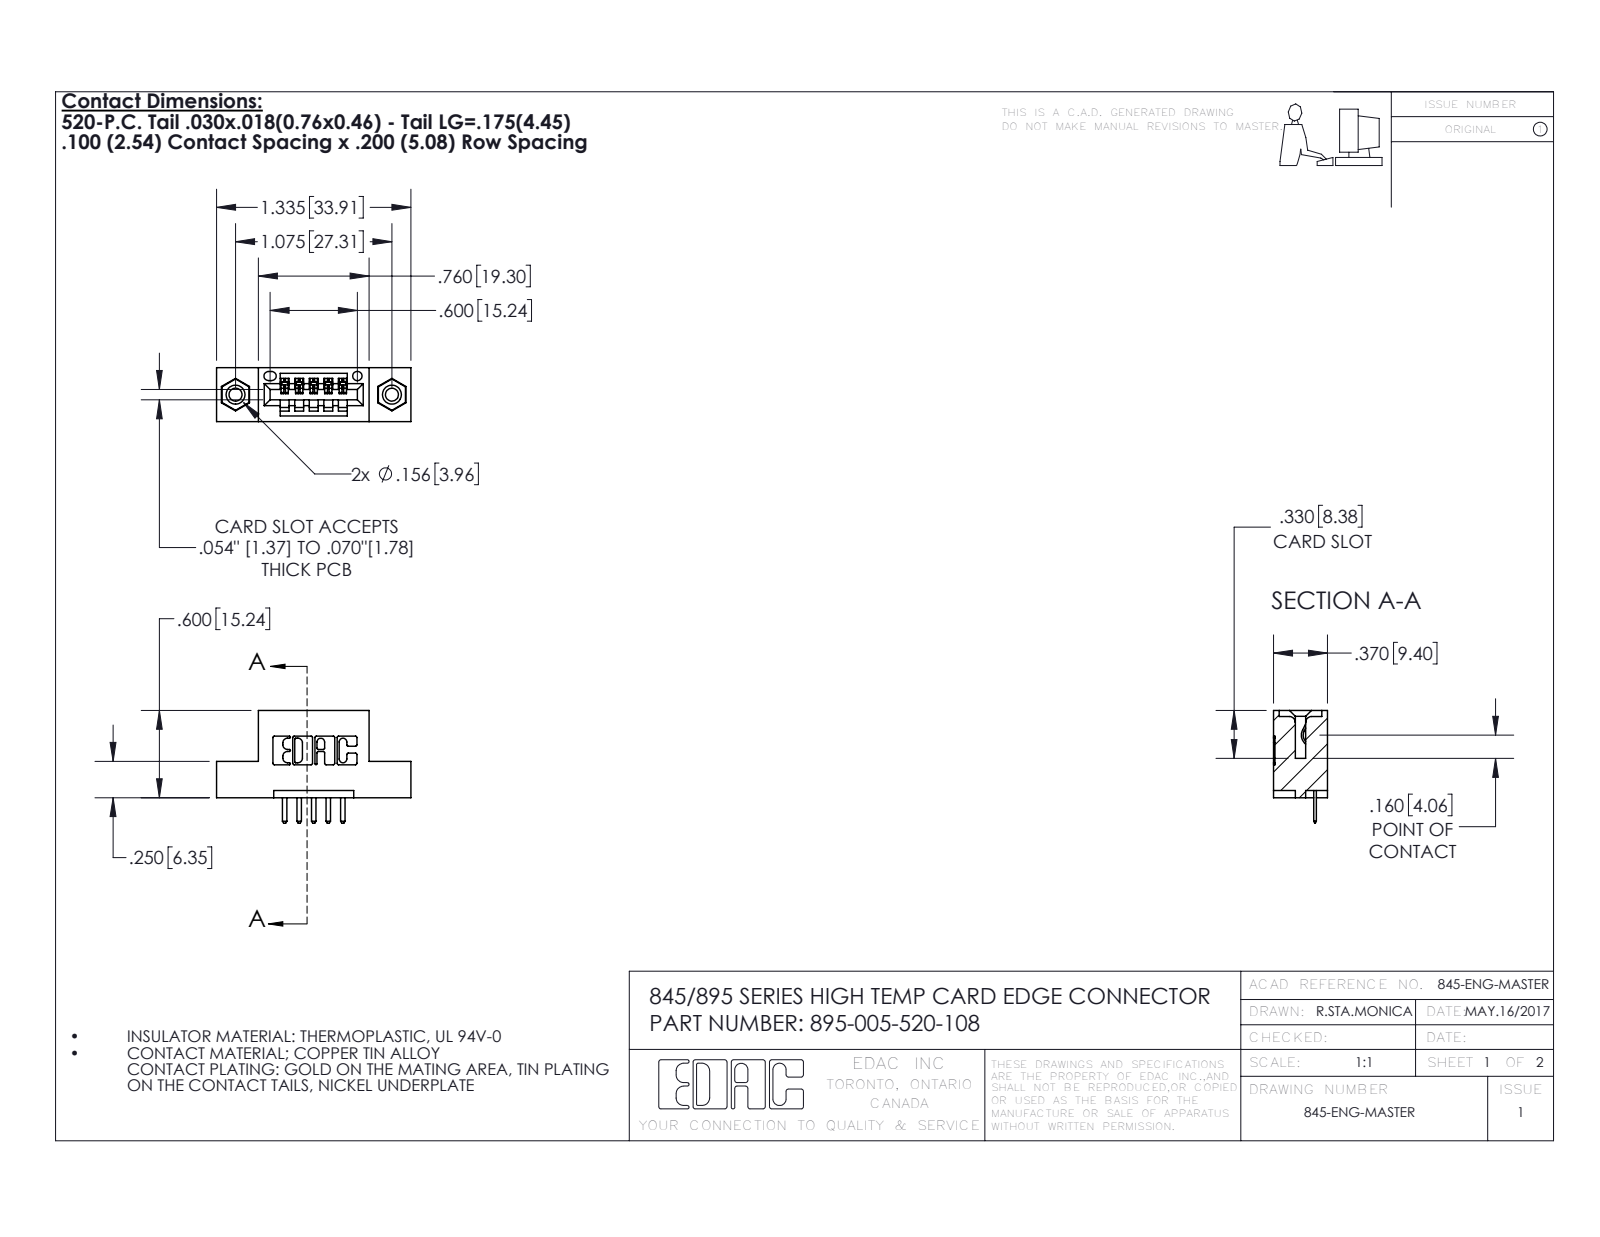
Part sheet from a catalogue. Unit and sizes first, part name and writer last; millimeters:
Units: millimetres
Overall size (bounding box): 33.9 × 19.7 × 9.4
Round holes (diameter × count): ⌀2.3 ×2, ⌀3.2 ×2, ⌀4 ×2, ⌀1.6 ×1
Round bosses / shafts (diameter × count): ⌀3.9 ×2
Partial cylindrical surfaces — rounded edges, fillets, slot ends (radius × count): R0.3 ×22, R0.3 ×12, R0.2 ×10, R0.2 ×6, R0.8 ×6, R0.7 ×3, R0.8 ×2, R1 ×2
Main face-to-face distances: 5.1, 9.4, 2.5, 1.8, 7.6, 8.9, 6.4, 1.5, 14, 0.6
Hole centre spacings: 6.9, 21.5, 27.3
Volume: 2 900 mm³ · Surface area: 3 319 mm²
Bodies: 8 solids, 496 faces (322 planar, 158 cylindrical, 16 other)
Part name (STEP PRODUCT): 395-005-520-108; 345 Part_Flush Mounting Lugs - 0.156 Dia-TI; 345-250-001_345-250-003-102; 345-292-001_345-293-120
STEP written by: SolidWorks 2016 (CONFIG_CONTROL_DESIGN)
